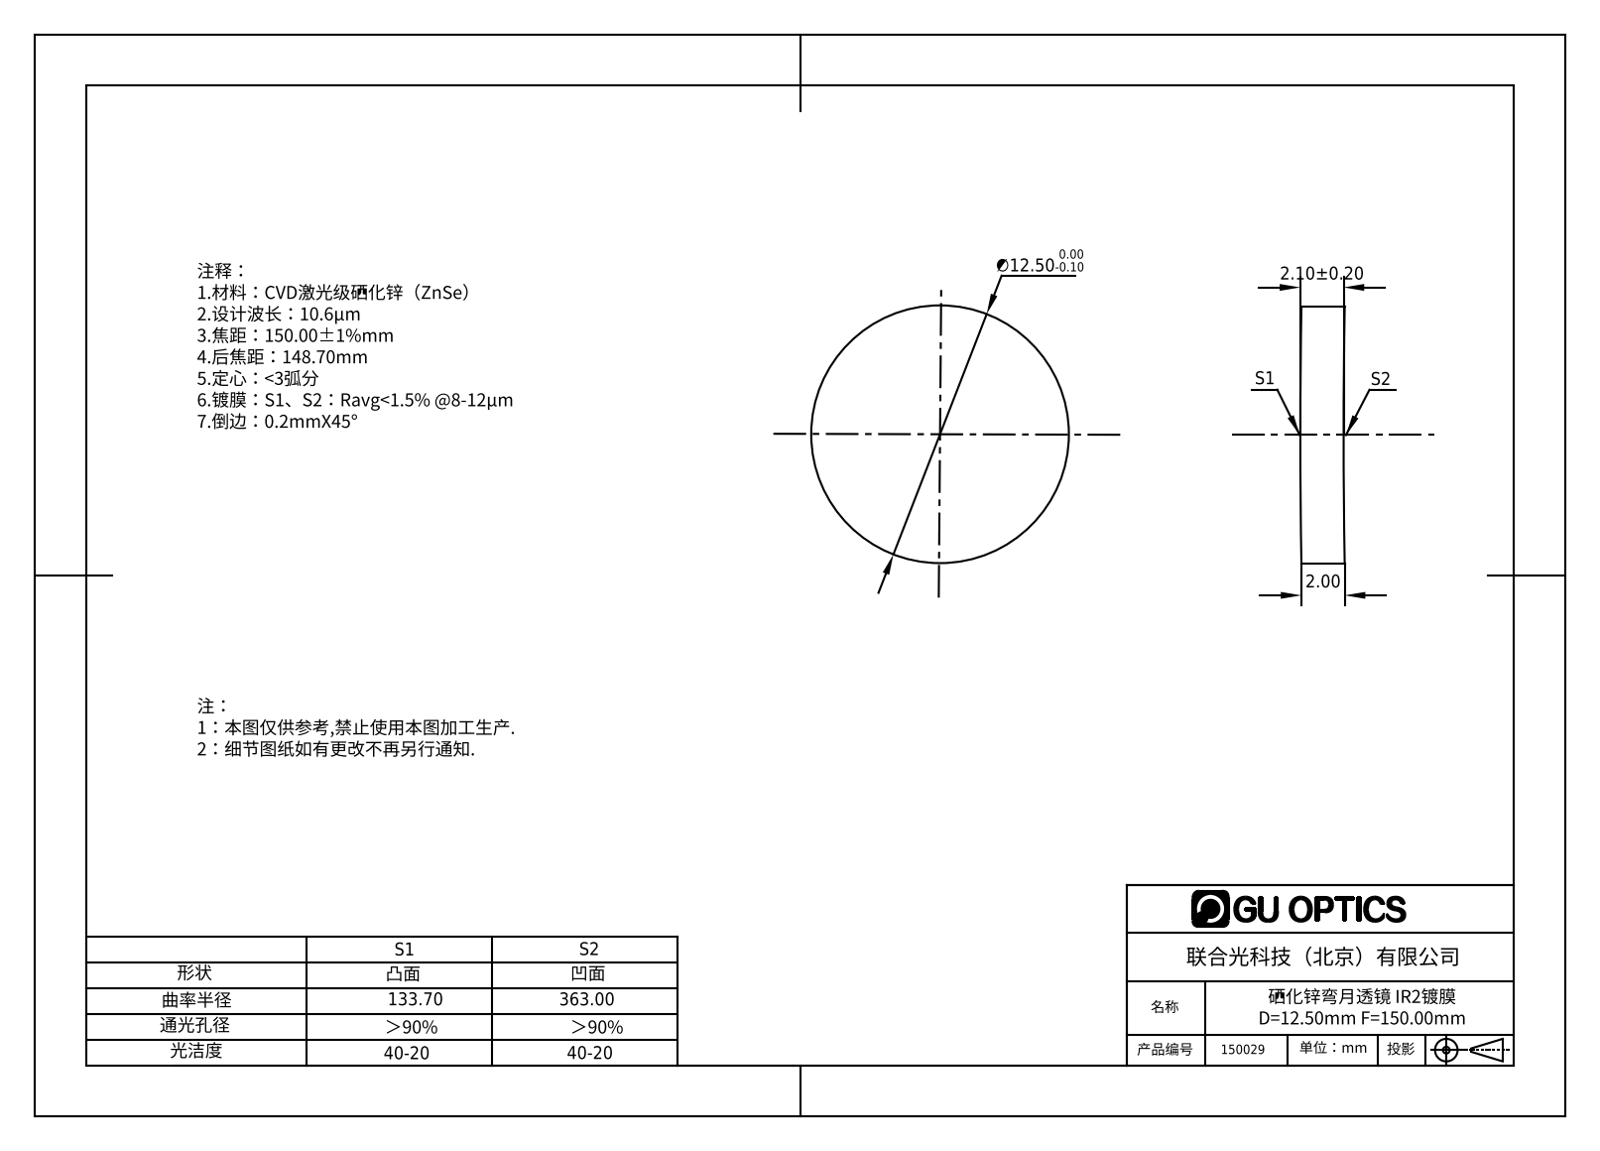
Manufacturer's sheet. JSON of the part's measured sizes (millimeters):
{"part_name": "150004", "step_written_by": "SolidWorks 2016 (AUTOMOTIVE_DESIGN)", "units": "millimeters", "bodies": {"solids": 1, "faces": 6, "planar": 0, "cylindrical": 2, "other": 4}, "overall_size": [12.5, 12.5, 2.15], "volume_mm3": 258, "surface_area_mm2": 328, "round_bosses_or_shafts": [[12.5, 1]]}
